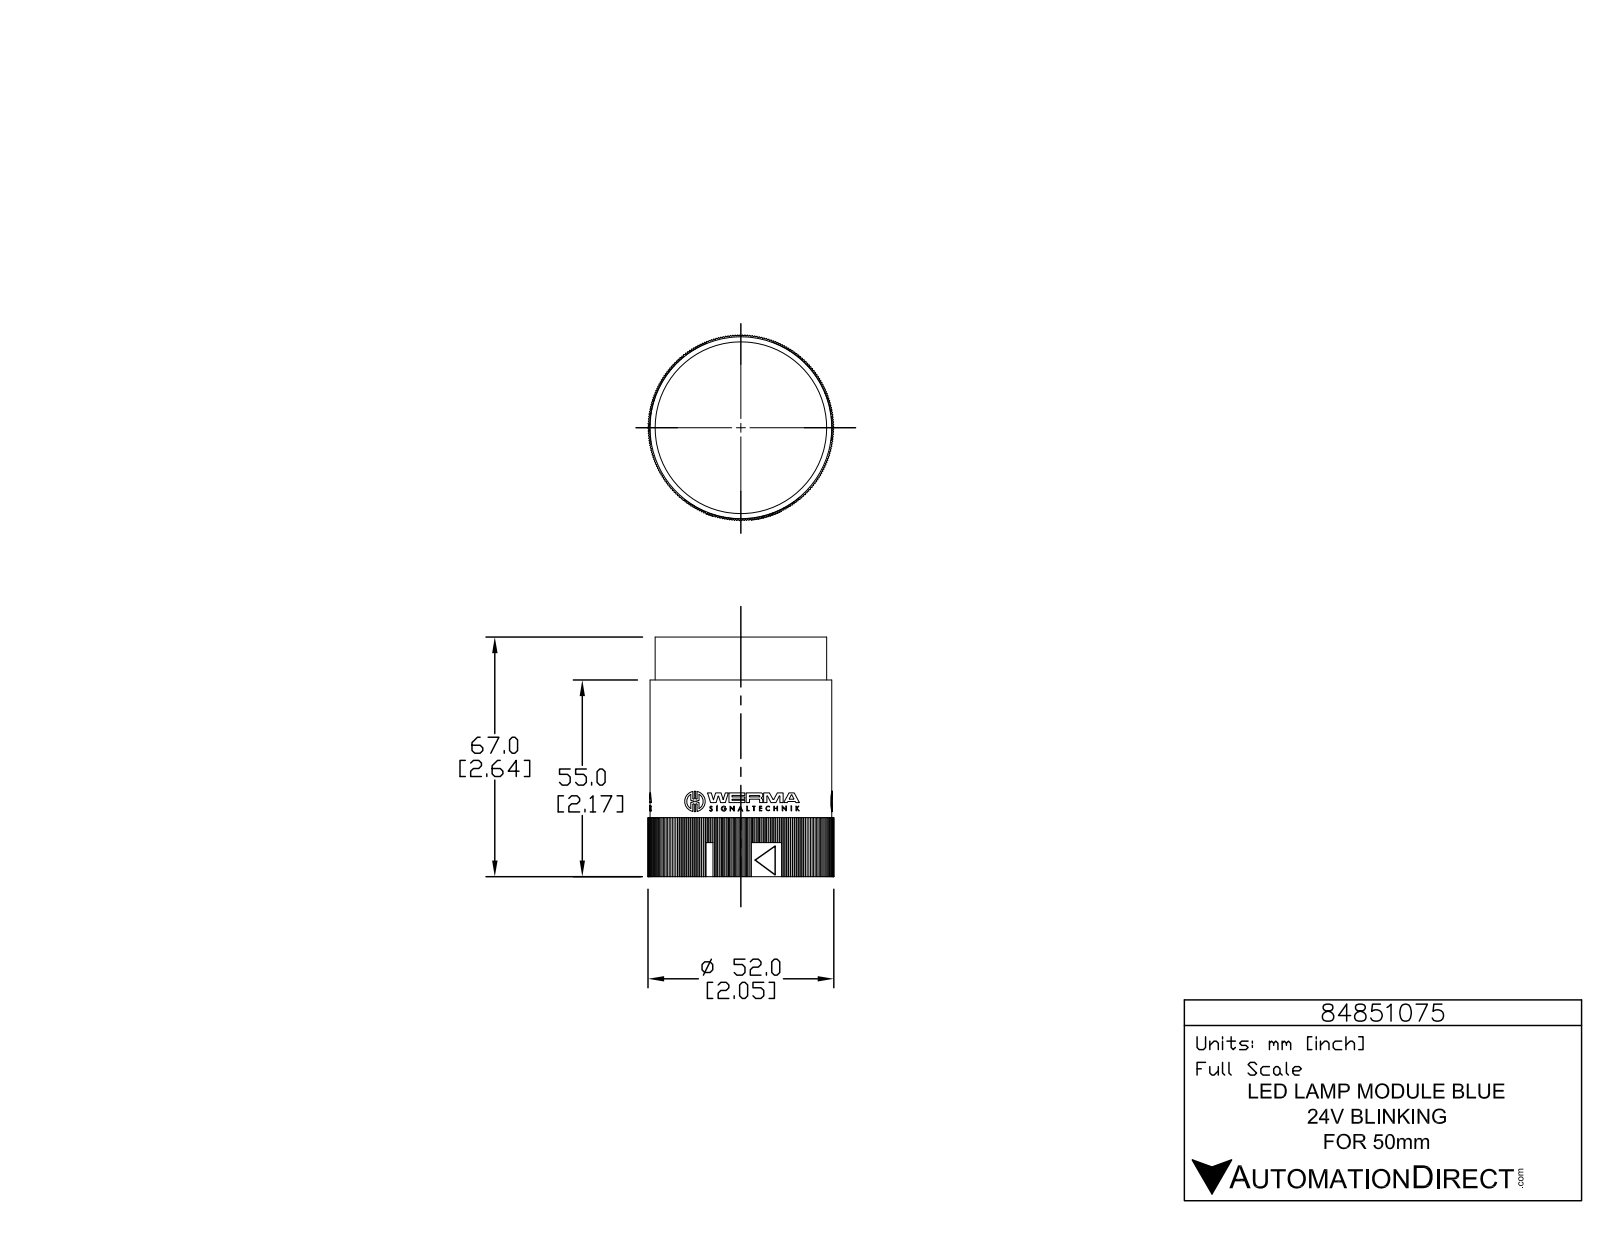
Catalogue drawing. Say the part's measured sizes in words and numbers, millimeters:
The part is named "84851075". Its 3-D file was written by "SolidWorks 2015 (AUTOMOTIVE_DESIGN)". It is 1 solid with 1265 faces: 1020 planar, 245 cylindrical and 0 other. Overall it measures 67 by 52 by 52 millimeters. Its volume is 112 600 cubic millimeters and its surface area 17 820 square millimeters. Round holes: 3 of diameter 1, 1 of diameter 48.2. Round bosses or shafts: 3 of diameter 5.7, 3 of diameter 1.4, 1 of diameter 50.9, 1 of diameter 48. Partial cylindrical surfaces (rounded edges, fillets, slot ends): 6 of radius 0.2, 6 of radius 0.2, 6 of radius 0.2, 6 of radius 3.3, 3 of radius 0.1, 3 of radius 0.1, 3 of radius 0.2, 3 of radius 0.2. The main face-to-face distances are 55, 36.3, 36.3, 36.3, 12, 67, 36.3, 36.3, 43, 50.5.
